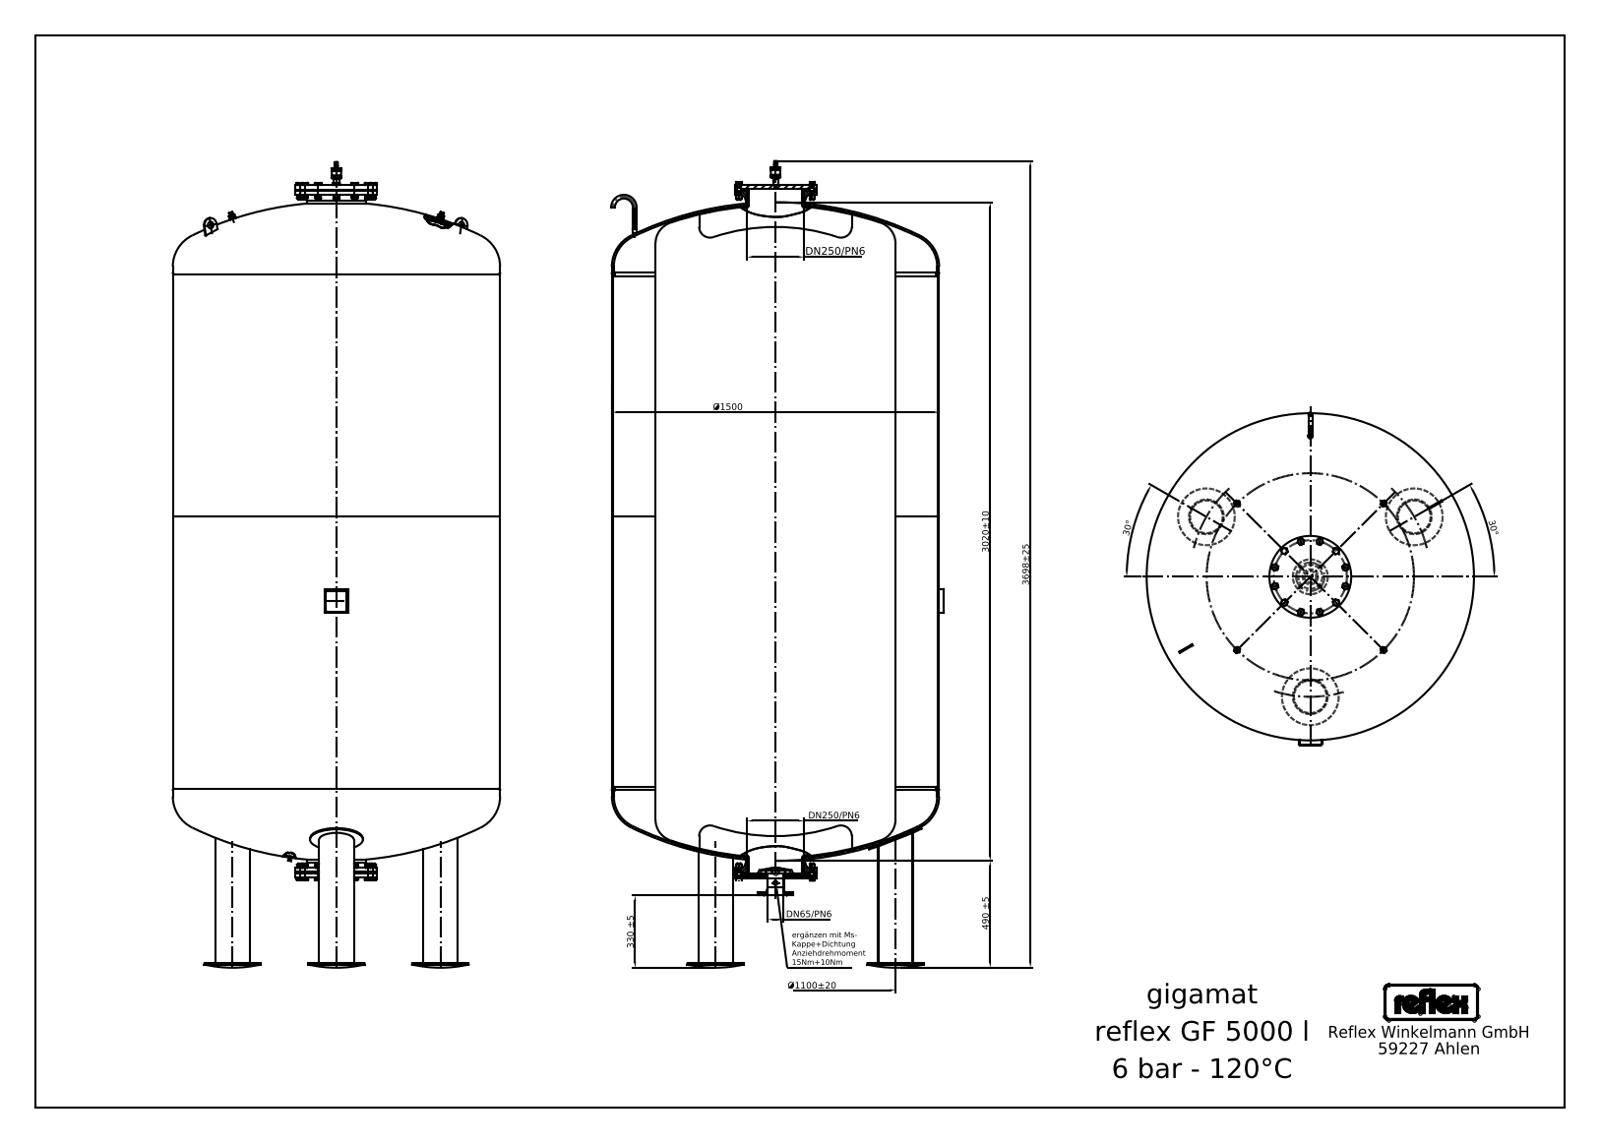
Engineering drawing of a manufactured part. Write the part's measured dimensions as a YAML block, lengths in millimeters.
step_written_by: "Mechanical Desktop 2008 (CONFIG_CONTROL_DESIGN)"
units: millimeters
bodies: {solids: 20, faces: 812, planar: 487, cylindrical: 199, other: 126}
overall_size: [3698, 1500, 1500]
volume: 5023000000
surface_area: 25510000
round_holes:
  - {diameter: 30, count: 1}
  - {diameter: 260.4, count: 1}
round_bosses_or_shafts:
  - {diameter: 16, count: 12}
  - {diameter: 159, count: 3}
  - {diameter: 16.6, count: 2}
  - {diameter: 12, count: 2}
  - {diameter: 1500, count: 1}
  - {diameter: 375, count: 1}
  - {diameter: 273, count: 1}
  - {diameter: 272.4, count: 1}
partial_cylinders:
  - {radius: 8.44, count: 4}
  - {radius: 3.38, count: 3}
  - {radius: 5.76, count: 2}
  - {radius: 10.12, count: 2}
  - {radius: 13.91, count: 2}
  - {radius: 14.1, count: 2}
  - {radius: 19.06, count: 2}
  - {radius: 4.22, count: 1}
face_to_face_distances: [2360, 22, 3156, 27, 3129, 2749, 389, 2771, 411, 407]
